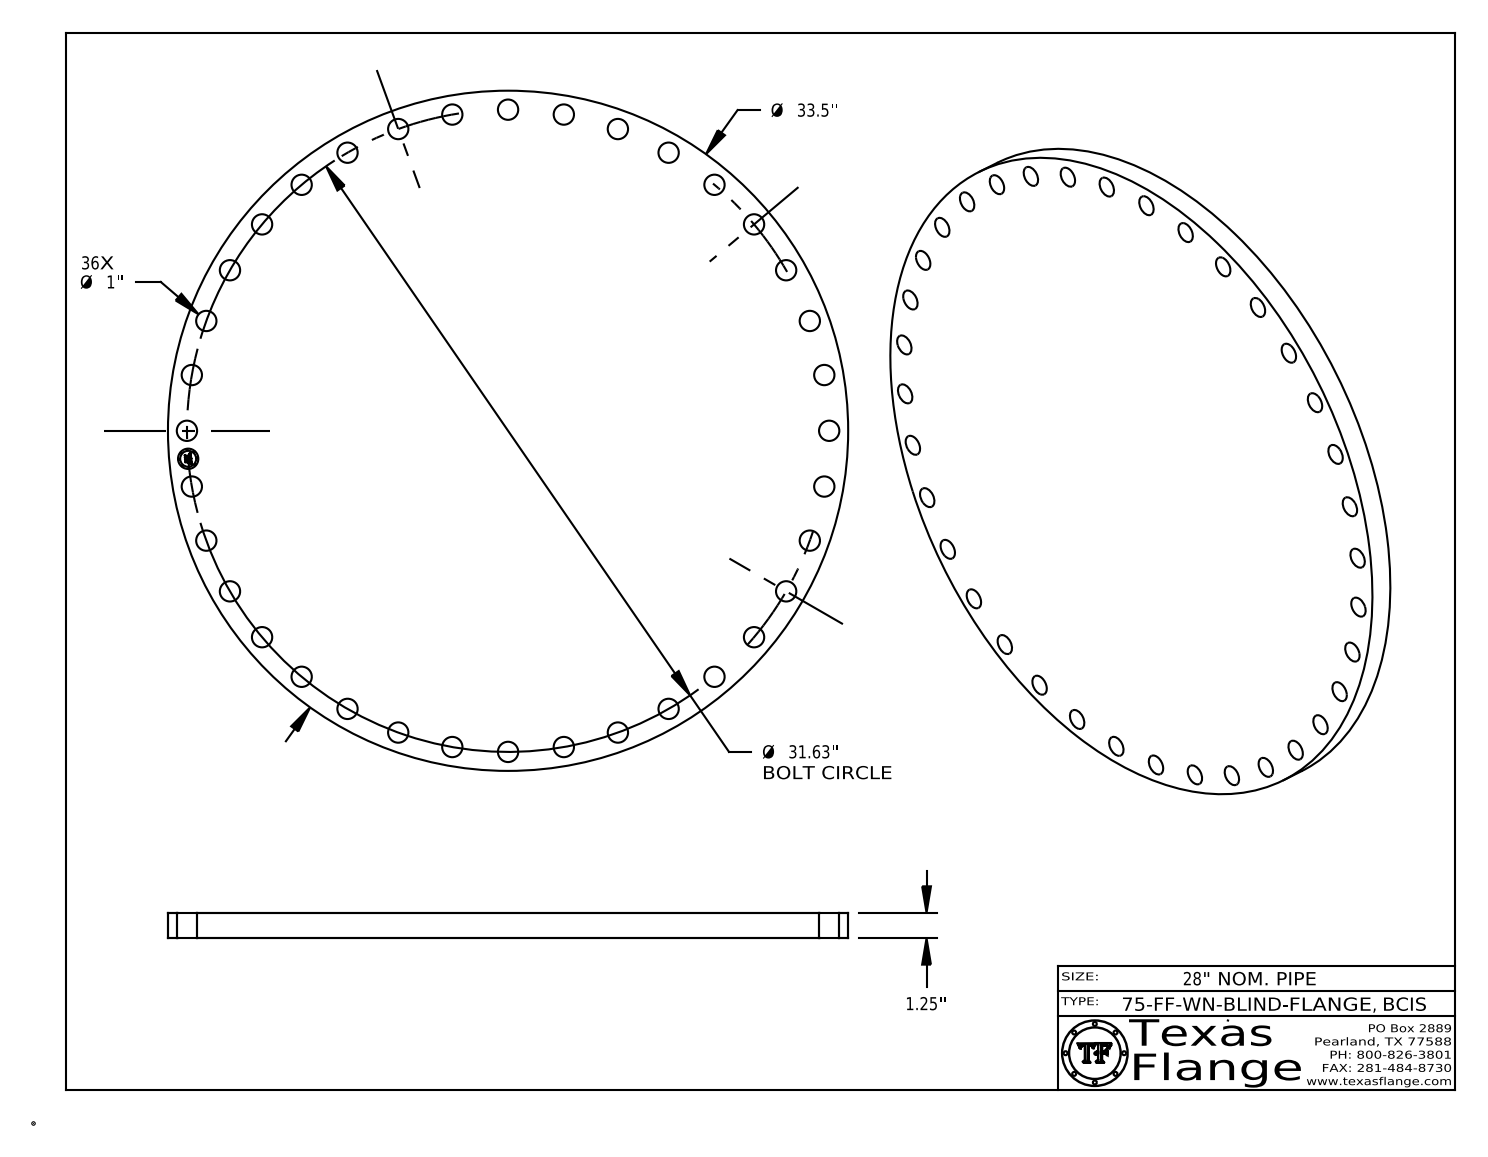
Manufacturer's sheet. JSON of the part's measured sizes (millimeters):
{"part_name": "75-FF-WN-BLIND, Series BCIS", "step_written_by": "CATIA V5 STEP AP214 (AUTOMOTIVE_DESIGN)", "units": "millimeters", "bodies": {"solids": 1, "faces": 461, "planar": 367, "cylindrical": 94, "other": 0}, "overall_size": [850.9, 850.9, 31.8], "volume_mm3": 17470000, "surface_area_mm2": 1277000, "round_holes": [[25.4, 37]], "round_bosses_or_shafts": [[1.5, 8], [850.9, 1], [20, 1]], "face_to_face_distances": [31.8, 0.4, 31.4, 7.6, 7.4, 1.4, 4.9, 6.3, 1.1, 3.8], "hole_center_spacings": [139.5, 274.8, 70, 339.5, 728.1, 754.9, 401.7, 615.4]}
